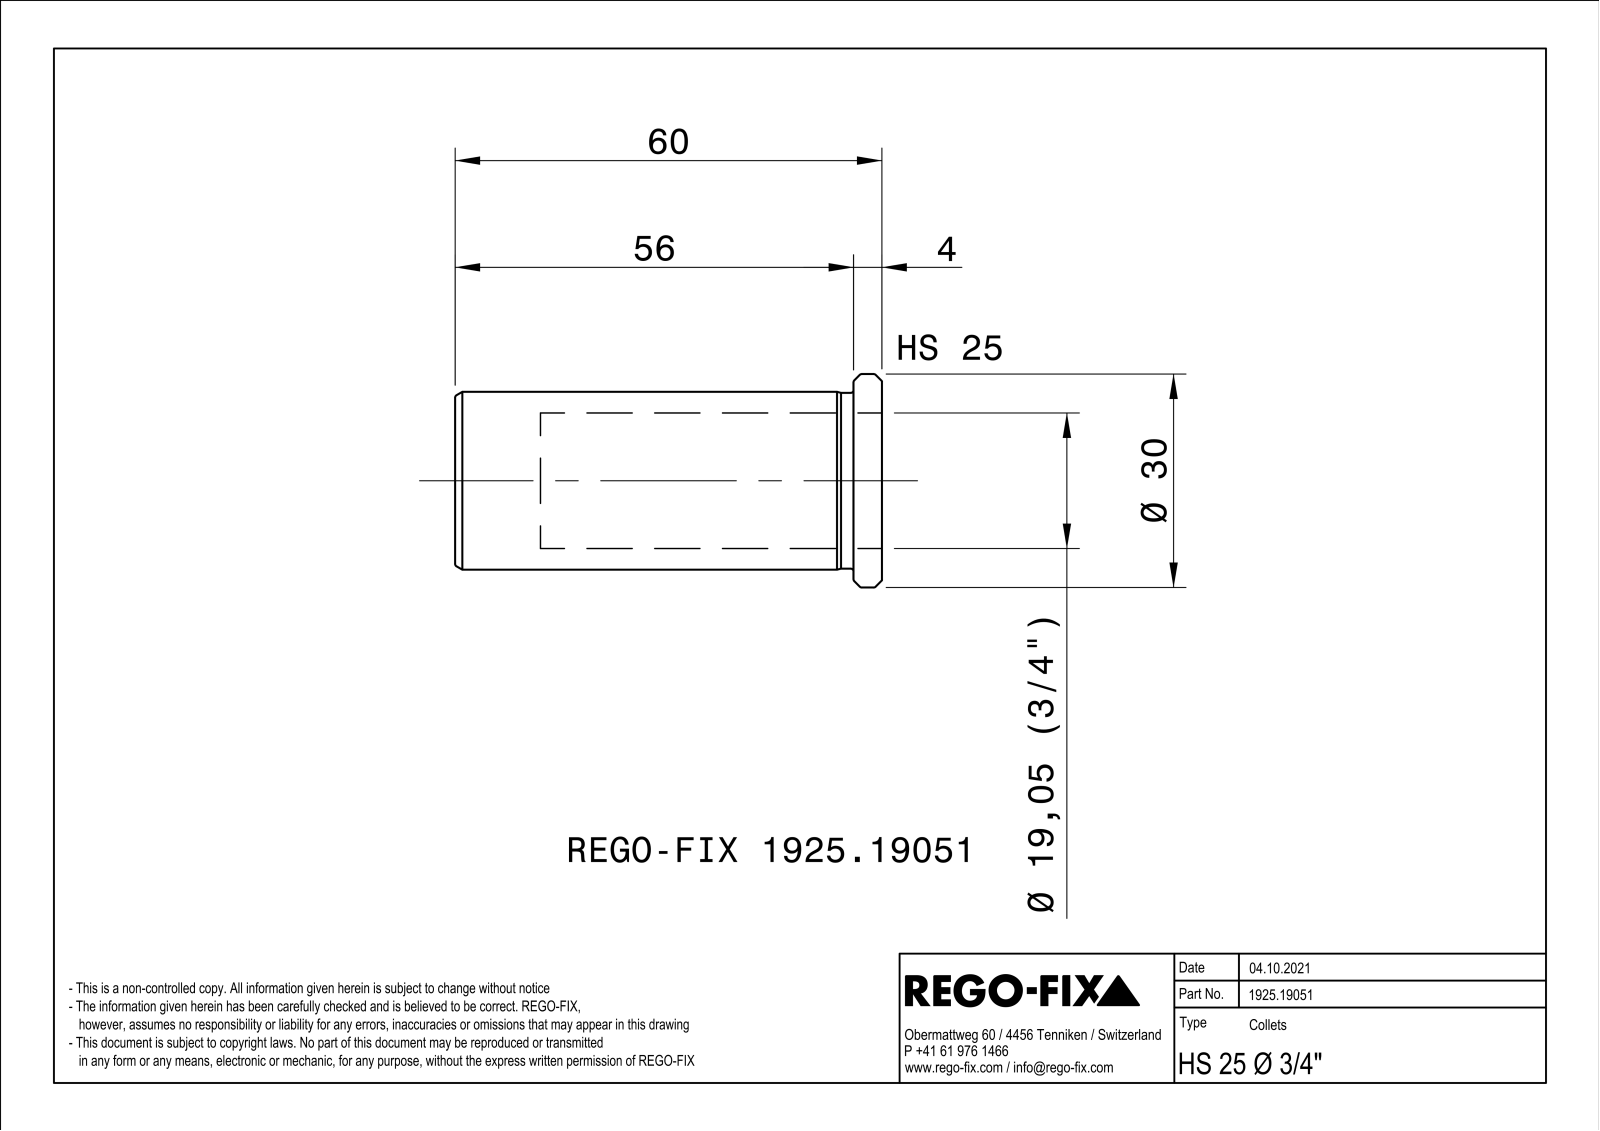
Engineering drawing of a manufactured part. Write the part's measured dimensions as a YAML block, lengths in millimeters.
part_name: "NOCUT"
step_written_by: "SIEMENS PLM Software Solid Edge ST10 (AUTOMOTIVE_DESIGN)"
units: millimeters
bodies: {solids: 1, faces: 71, planar: 22, cylindrical: 11, other: 38}
overall_size: [60, 29.98, 29.98]
volume: 12144
surface_area: 9688
round_holes:
  - {diameter: 19.05, count: 1}
  - {diameter: 20.5, count: 1}
round_bosses_or_shafts:
  - {diameter: 30, count: 1}
  - {diameter: 25, count: 1}
  - {diameter: 24.7, count: 1}
face_to_face_distances: [1, 4, 60, 56]
